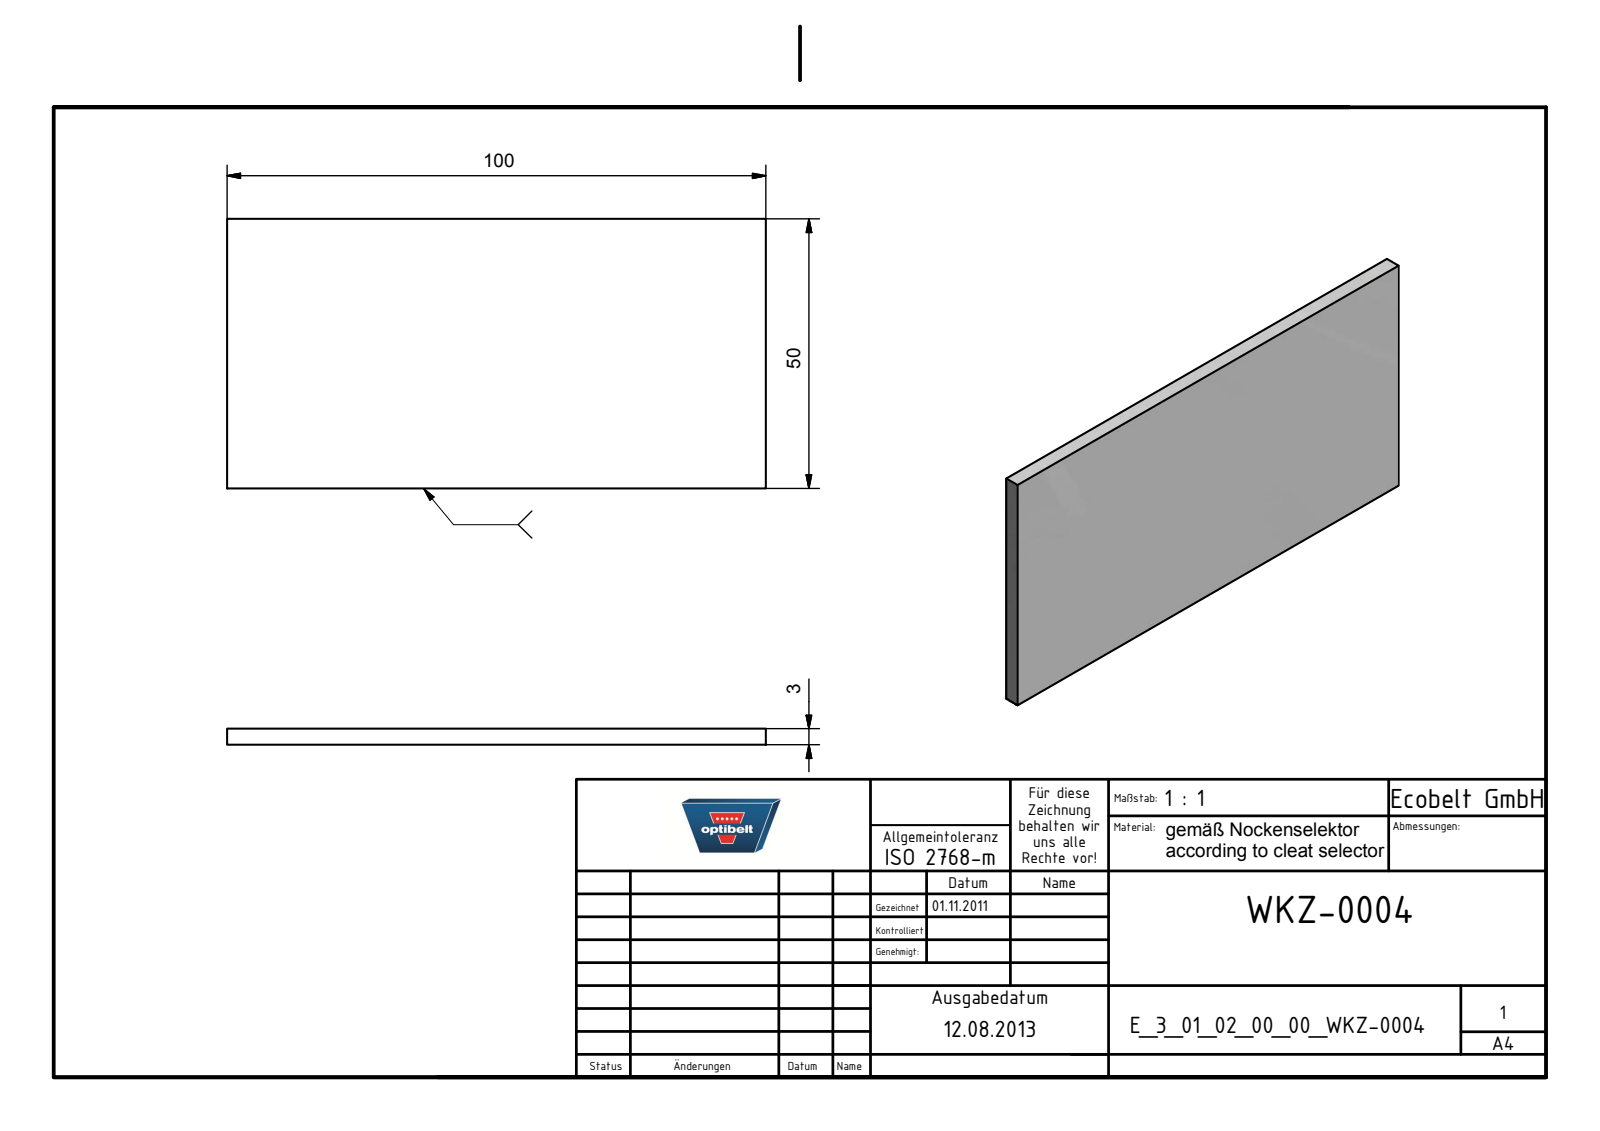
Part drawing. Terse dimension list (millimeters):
name: E_3_01_02_00_00_WKZ-0004
written by: Autodesk Inventor 2021 (AUTOMOTIVE_DESIGN)
unit: mm
bodies: 1 solid, 6 faces (6 planar, 0 cylindrical, 0 other)
size: 100 × 50 × 3
volume: 15 000 mm³; area: 10 900 mm²
face distances: 3, 50, 100
